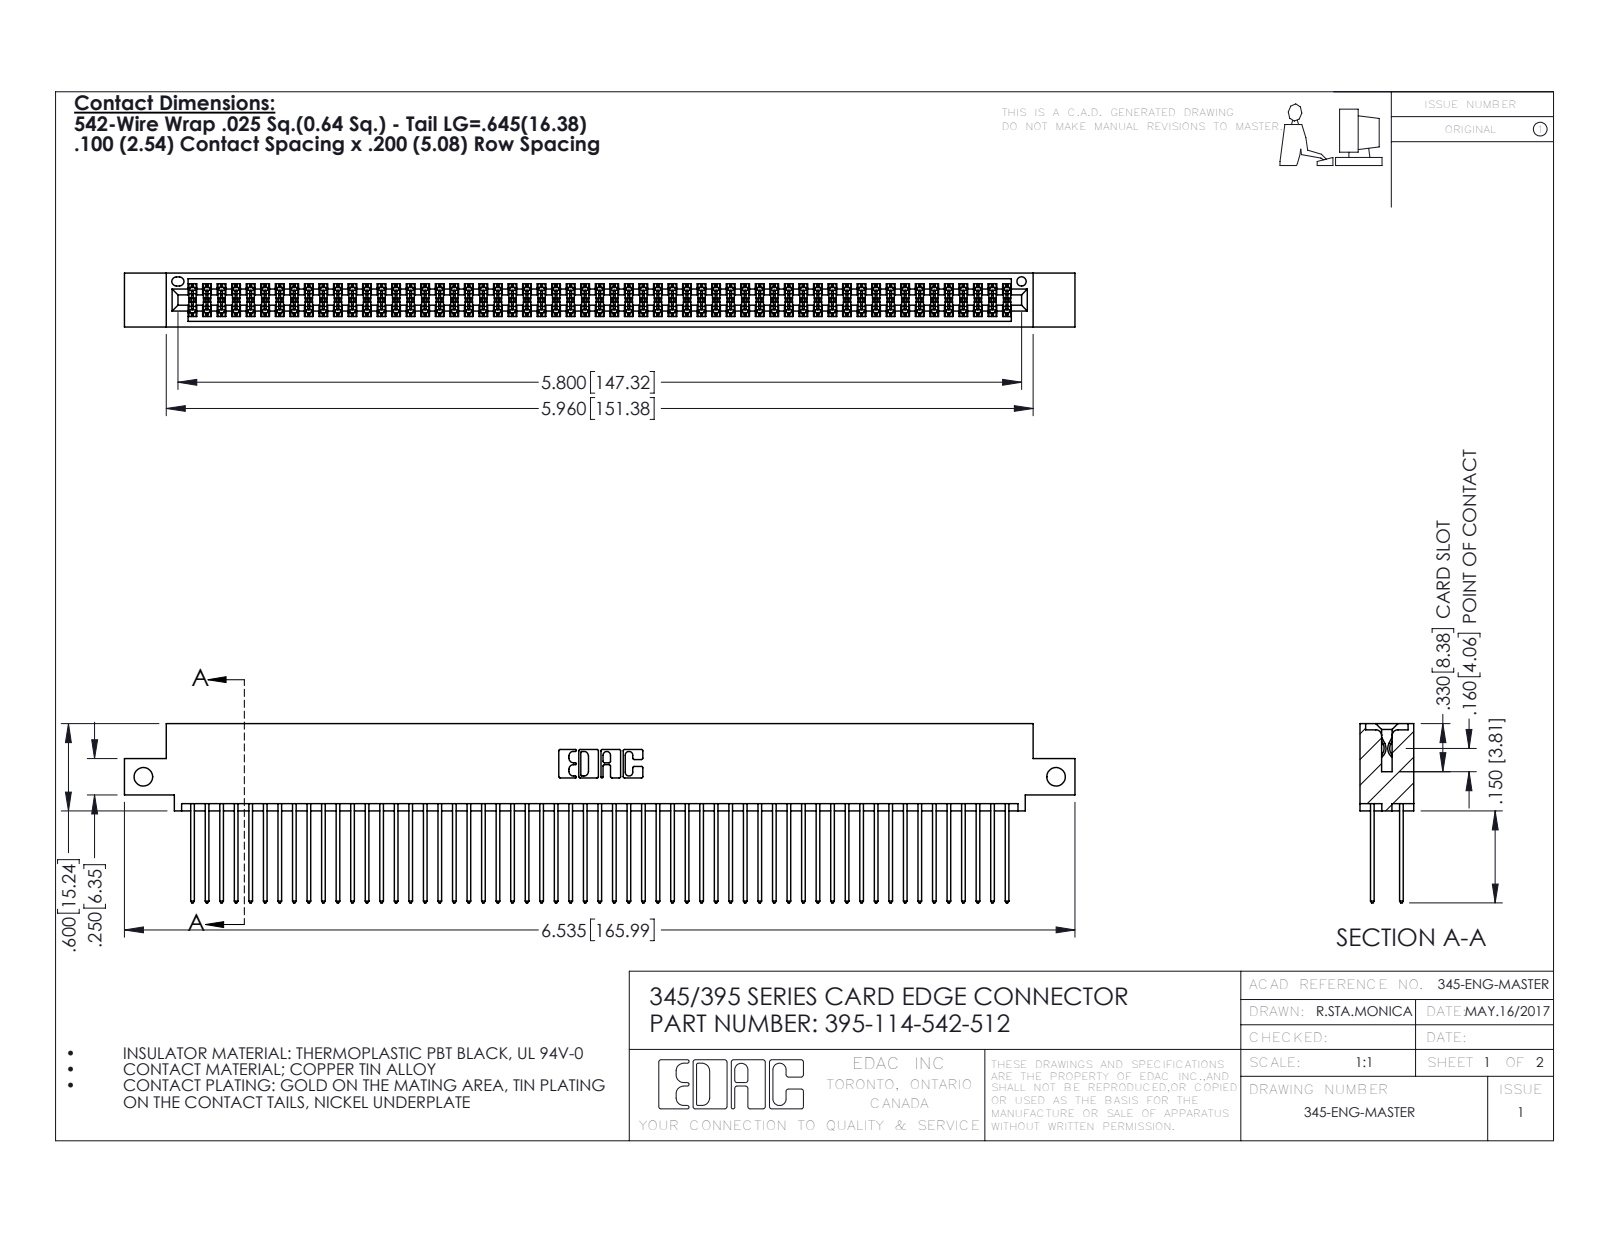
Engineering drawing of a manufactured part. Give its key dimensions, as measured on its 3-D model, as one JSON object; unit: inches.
{"part_name": "345 Part_0.110 Offset - Side Mount; 345-292-001_345-293-142; 395-114-542-512", "step_written_by": "SolidWorks 2016 (CONFIG_CONTROL_DESIGN)", "units": "inches", "bodies": {"solids": 115, "faces": 5830, "planar": 3846, "cylindrical": 1984, "other": 0}, "overall_size": [6.535, 1.232, 0.37], "volume_in3": 1.015, "surface_area_in2": 42.35, "round_holes": [[0.128, 2], [0.064, 1]], "partial_cylinders_radius": [[0.006, 171], [0.01, 114], [0.01, 22], [0.007, 6], [0.031, 6], [0.026, 3], [0.014, 2], [0.019, 2]], "face_to_face_distances": [0.072, 0.298, 0.2, 0.098, 0.272, 0.025, 0.225, 0.37, 0.175, 0.149], "hole_center_spacings": [6.275]}
